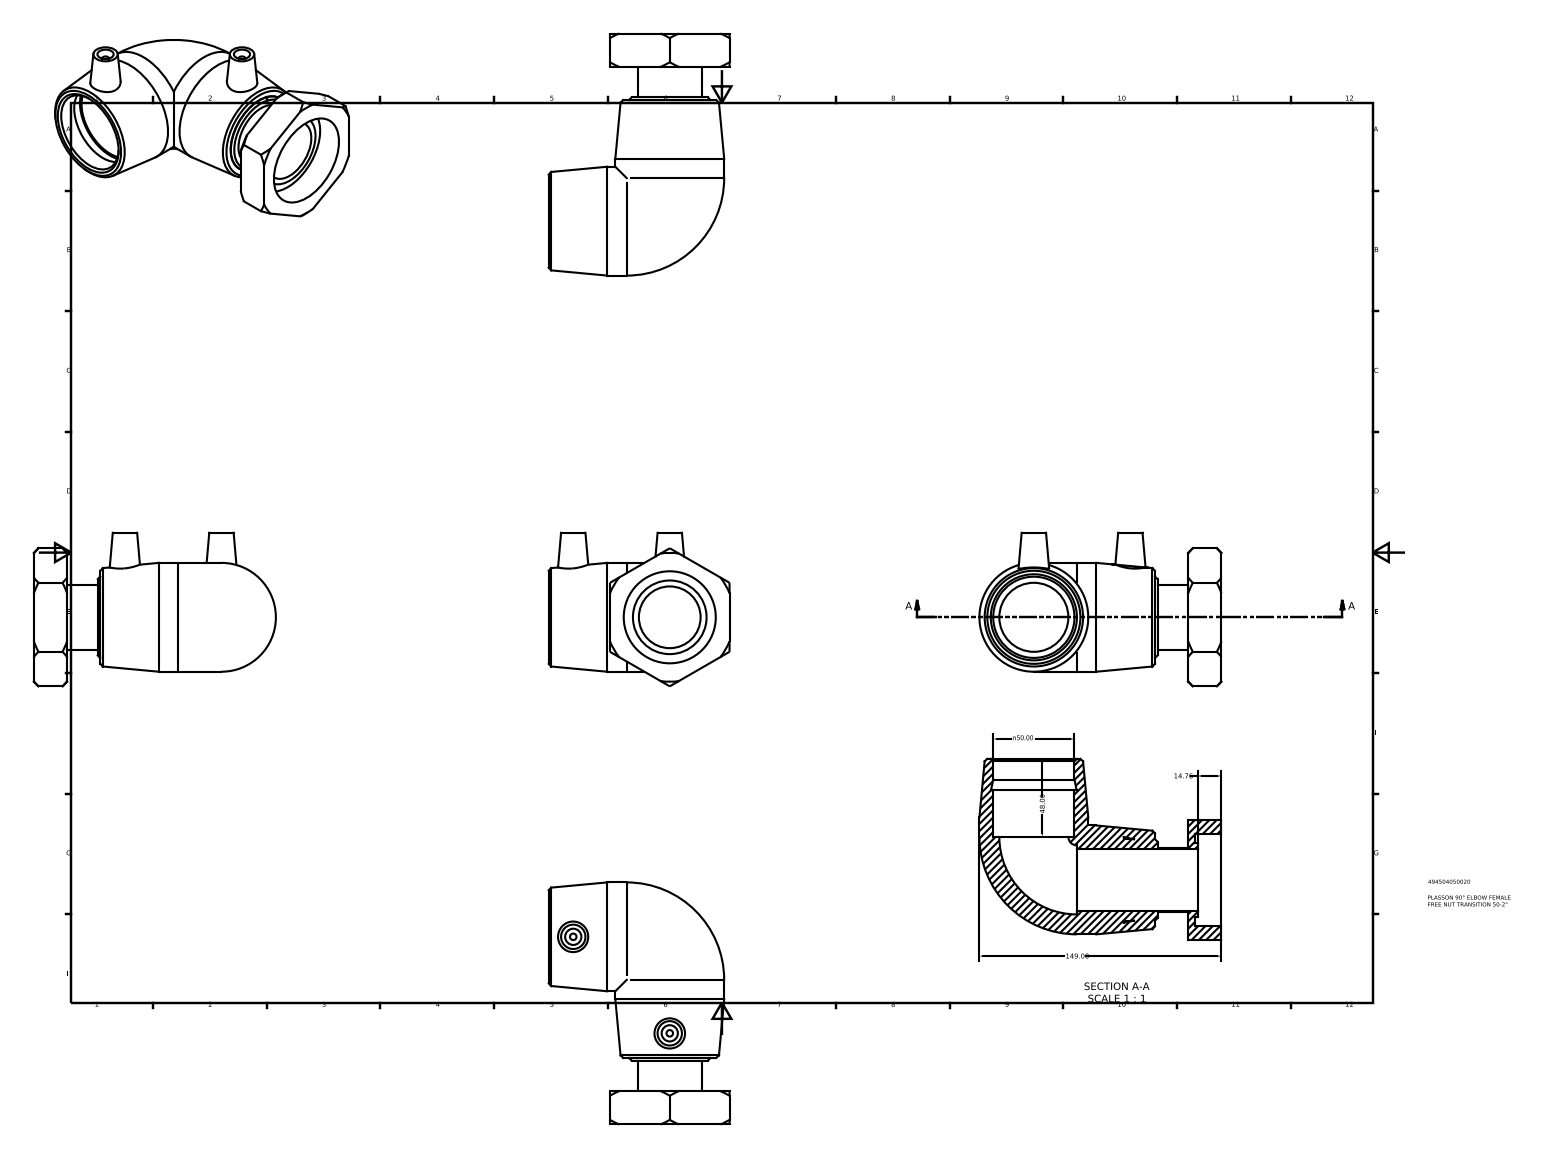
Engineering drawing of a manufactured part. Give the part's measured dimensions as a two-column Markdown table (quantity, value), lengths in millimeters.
| quantity | value |
| --- | --- |
| part name | 494504050020 |
| STEP written by | Autodesk Inventor 2015 (AUTOMOTIVE_DESIGN) |
| units | millimeters |
| bodies | 1 solid, 61 faces (23 planar, 14 cylindrical, 24 other) |
| overall size | 149 × 111.3 × 94.49 |
| volume | 314 059 mm³ |
| surface area | 76 540 mm² |
| round holes (diameter × count) | 10 × 2, 38 × 1, 50 × 1, 56.66 × 1 |
| round bosses / shafts (diameter × count) | 67 × 2, 4 × 2, 50 × 1, 45.32 × 1, 39.66 × 1 |
| main face-to-face distances | 20.5, 73.6, 24.6, 1.64, 4.1, 16.4, 48, 41, 10.3, 63.3 |
| hole center spacings | 84 |
